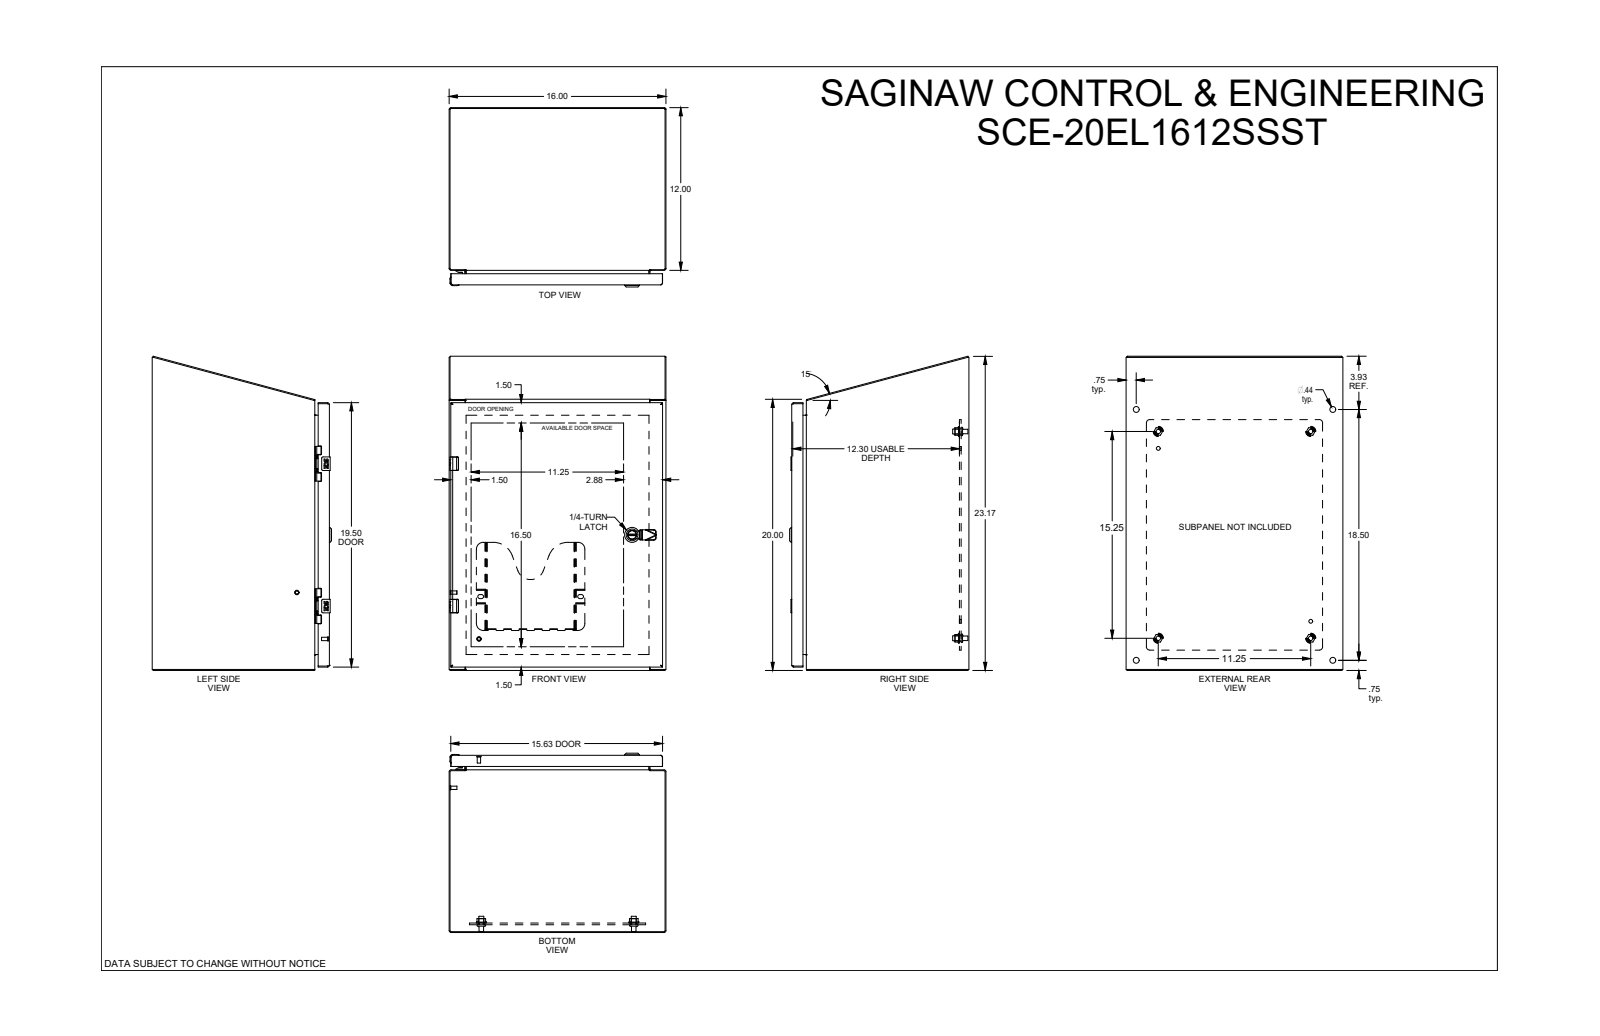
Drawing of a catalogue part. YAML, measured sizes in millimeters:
part_name: "SCE-20EL1612SSST_REV2"
step_written_by: "SolidWorks 2021 (AUTOMOTIVE_DESIGN)"
units: millimeters
bodies: {solids: 26, faces: 1333, planar: 619, cylindrical: 485, other: 229}
overall_size: [588.7, 406.4, 353.9]
volume: 2799000
surface_area: 2735000
round_holes:
  - {diameter: 4.4, count: 4}
  - {diameter: 5.2, count: 4}
  - {diameter: 6.2, count: 4}
  - {diameter: 6.8, count: 4}
  - {diameter: 9.5, count: 4}
  - {diameter: 11.1, count: 4}
  - {diameter: 12.7, count: 4}
  - {diameter: 4.7, count: 2}
  - {diameter: 5.5, count: 2}
  - {diameter: 7.1, count: 2}
  - {diameter: 4.9, count: 1}
  - {diameter: 5, count: 1}
round_bosses_or_shafts:
  - {diameter: 9.5, count: 4}
  - {diameter: 8.4, count: 4}
  - {diameter: 6.4, count: 4}
  - {diameter: 6.3, count: 4}
  - {diameter: 28, count: 1}
  - {diameter: 19.8, count: 1}
  - {diameter: 16, count: 1}
  - {diameter: 12.8, count: 1}
partial_cylinders:
  - {radius: 0.4, count: 28}
  - {radius: 1, count: 23}
  - {radius: 5.6, count: 16}
  - {radius: 1.5, count: 15}
  - {radius: 1.8, count: 10}
  - {radius: 3.7, count: 10}
  - {radius: 0.8, count: 8}
  - {radius: 0.8, count: 8}
face_to_face_distances: [1.9, 1.9, 404.5, 1.5, 330, 331.9, 330.4, 328.5, 406.4, 402.6]
hole_center_spacings: [266.7, 25, 329.2, 377.6, 384.3, 511.1, 333.7, 343.7]
